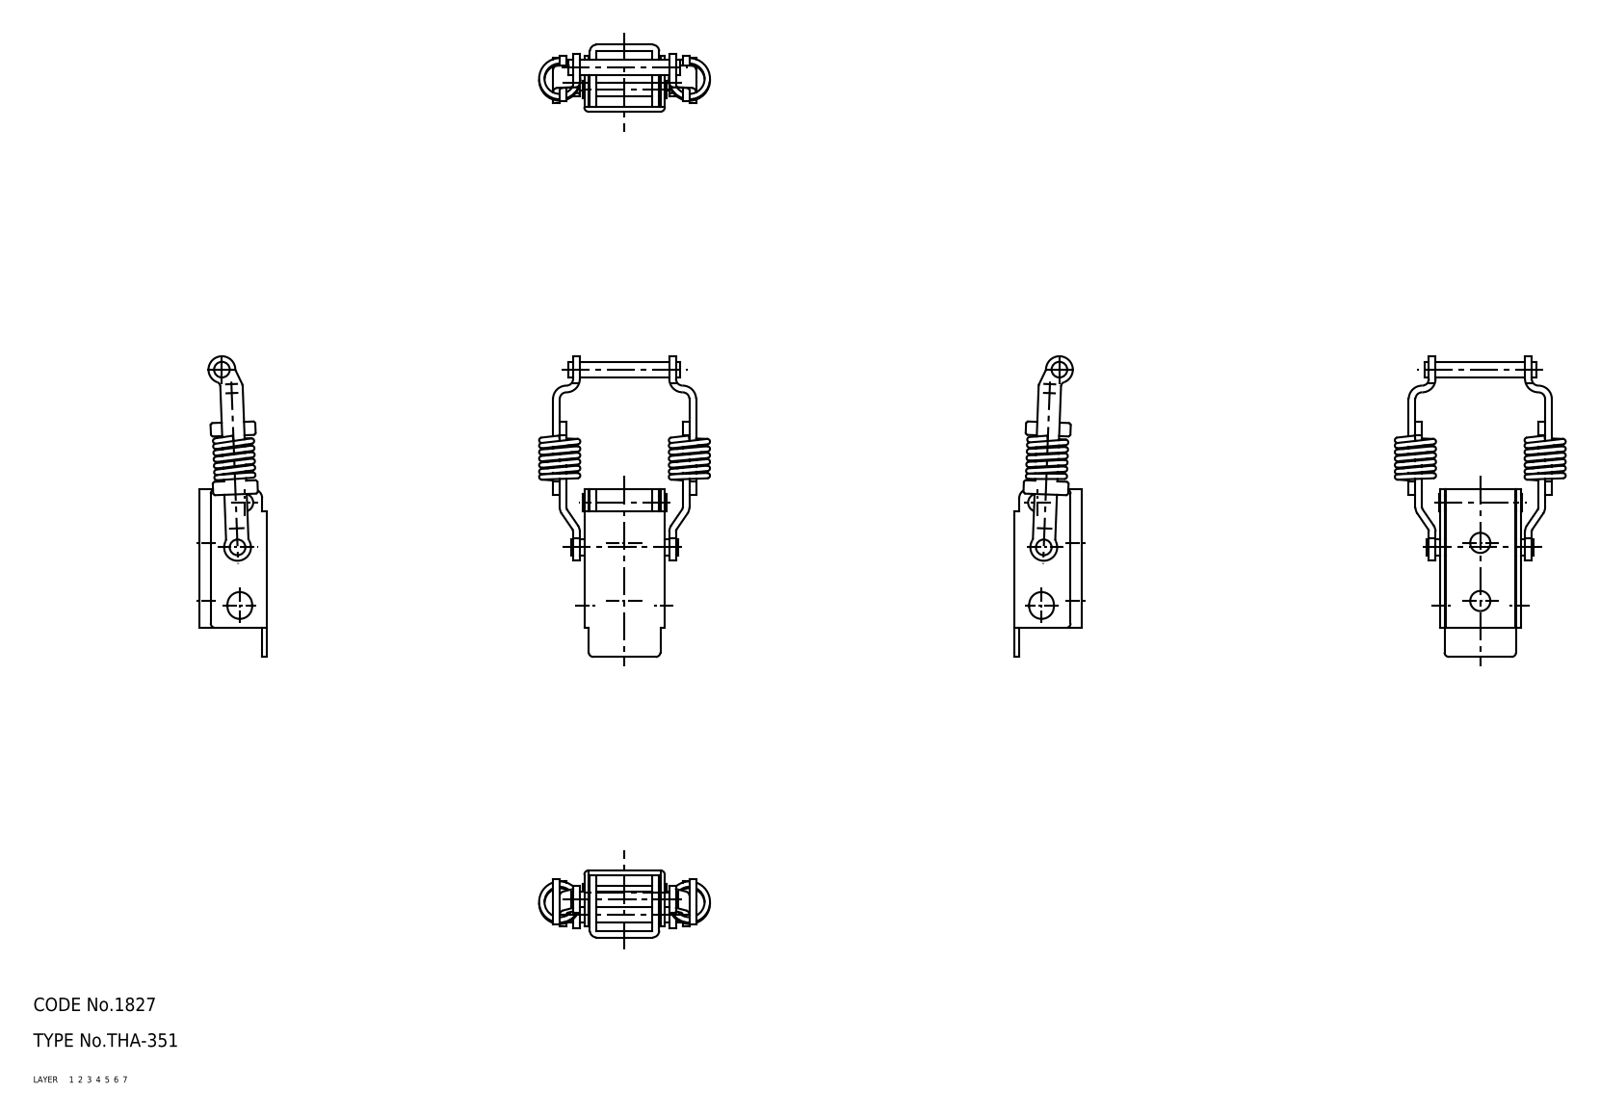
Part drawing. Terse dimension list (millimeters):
name: spring; shaft_A; arm_A_mr; shaft_B (+6 more)
written by: CADfix (AUTOMOTIVE_DESIGN)
unit: mm
bodies: 11 solids, 239 faces (0 planar, 0 cylindrical, 239 other)
size: 67.25 × 38.2 × 15
volume: 4 773 mm³; area: 9 178 mm²
